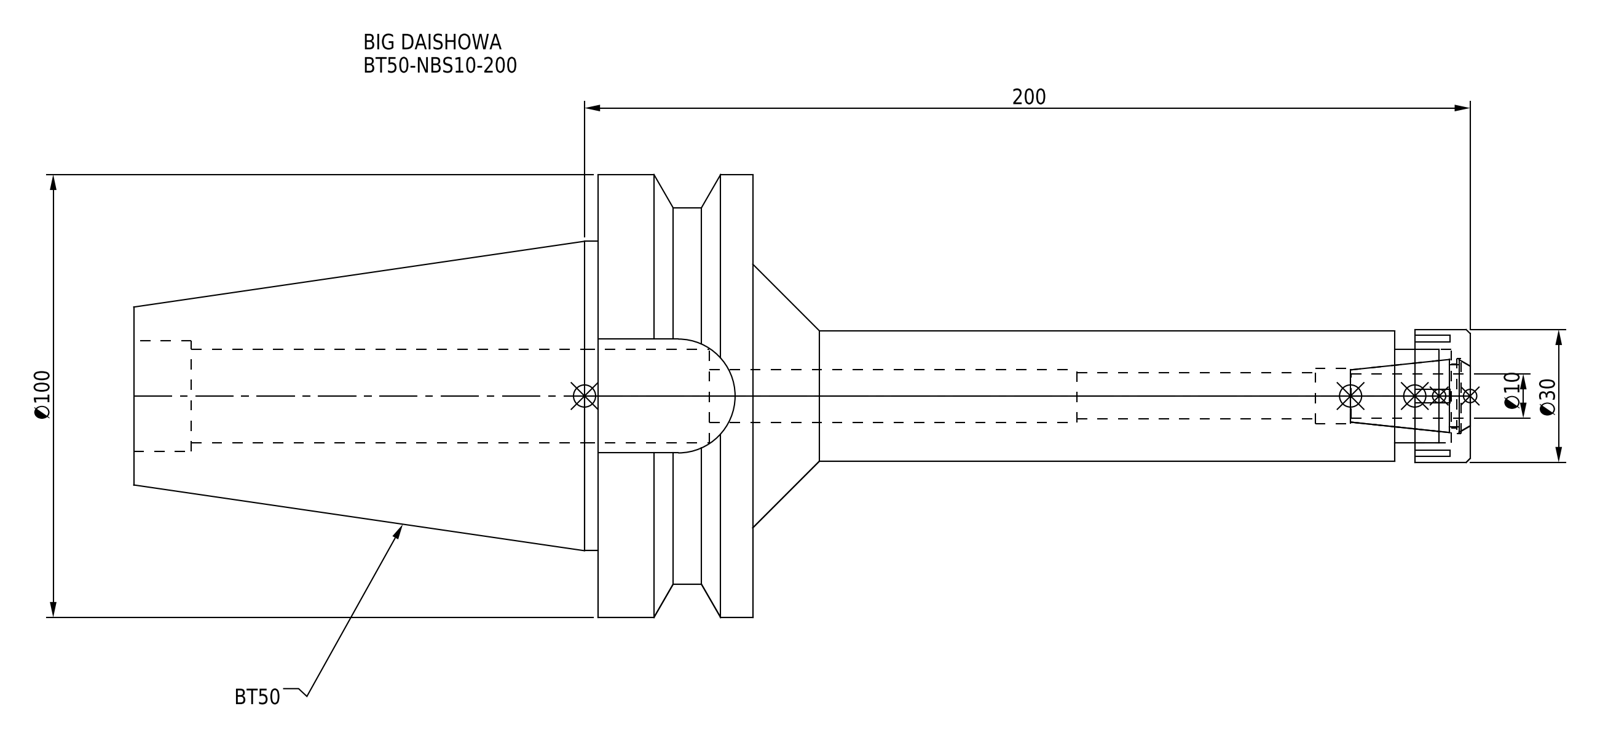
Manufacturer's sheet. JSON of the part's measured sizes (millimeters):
{"part_name": "DXF_TEMP_ASSY_ASM_4_ASM.stp; BT50-NBS10-200.stp; BT50-NBS10-200-FreeParts; BT50-NBS10-200_1.stp (+3 more)", "step_written_by": "SolidWorks 2019 (CONFIG_CONTROL_DESIGN)", "units": "millimeters", "bodies": {"solids": 2, "faces": 93, "planar": 45, "cylindrical": 34, "other": 14}, "overall_size": [301.8, 100, 100], "volume_mm3": 549779, "surface_area_mm2": 76640, "round_holes": [[10.4, 1], [12, 1], [12.5, 1], [14.5, 1], [17, 1], [21, 1], [21.2, 1], [25, 1]], "round_bosses_or_shafts": [[100, 1], [85, 1], [69.85, 1], [30, 1], [29.5, 1]], "partial_cylinders_radius": [[12.85, 1]], "face_to_face_distances": [35, 139.8, 104.8, 70.8, 162, 197, 301.8, 25.7, 4.5, 12.5]}
